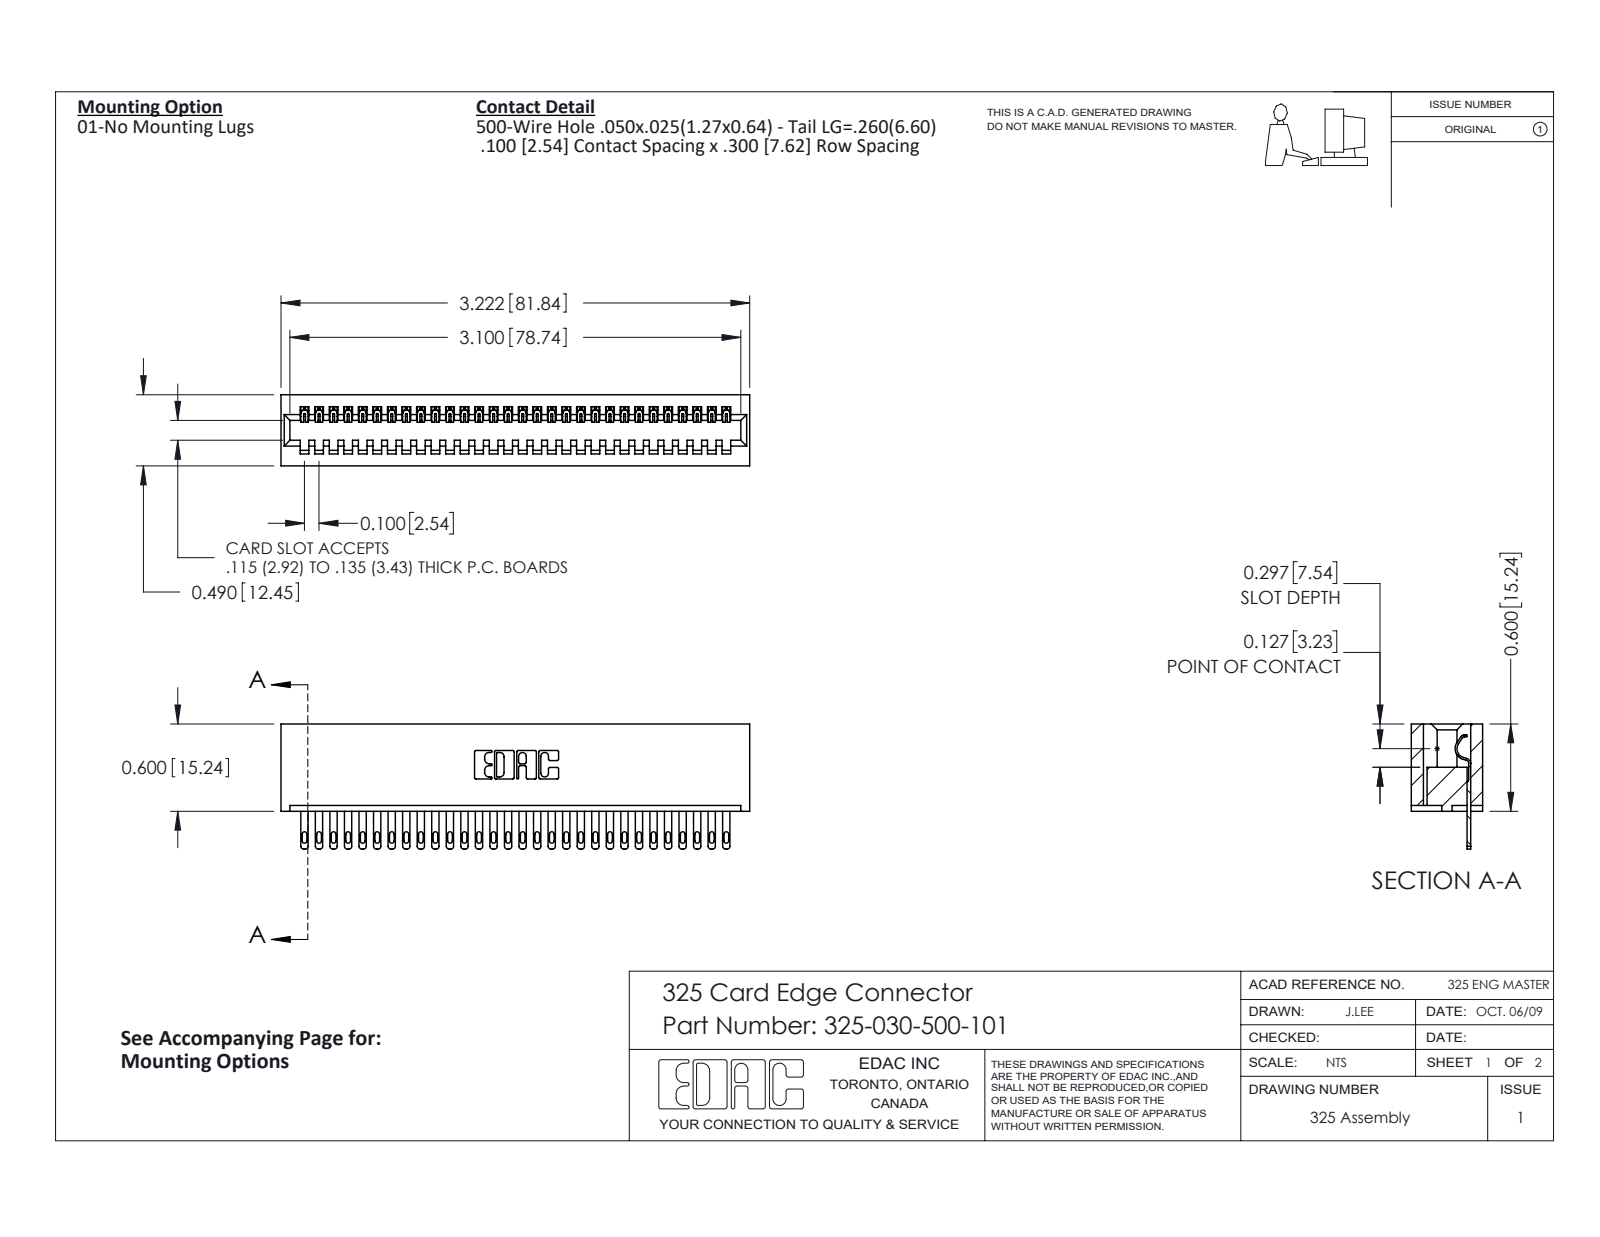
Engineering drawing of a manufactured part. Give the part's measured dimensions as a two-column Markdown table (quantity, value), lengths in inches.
| quantity | value |
| --- | --- |
| part name | 325-030-500-101; 325 Part_Lugless; 325-292-001_325-293-100 |
| STEP written by | SolidWorks 2016 (CONFIG_CONTROL_DESIGN) |
| units | inches |
| bodies | 31 solids, 1726 faces (1146 planar, 580 cylindrical, 0 other) |
| overall size | 3.222 × 0.86 × 0.49 |
| volume | 0.664 in³ |
| surface area | 18.99 in² |
| partial cylindrical surfaces (radius × count) | 0.006 × 60, 0.016 × 60, 0.02 × 60, 0.01 × 22, 0.007 × 6, 0.031 × 6, 0.026 × 3, 0.014 × 1 |
| main face-to-face distances | 0.083, 0.407, 0.3, 0.49, 0.107, 0.383, 0.025, 0.325, 0.1, 0.56 |
